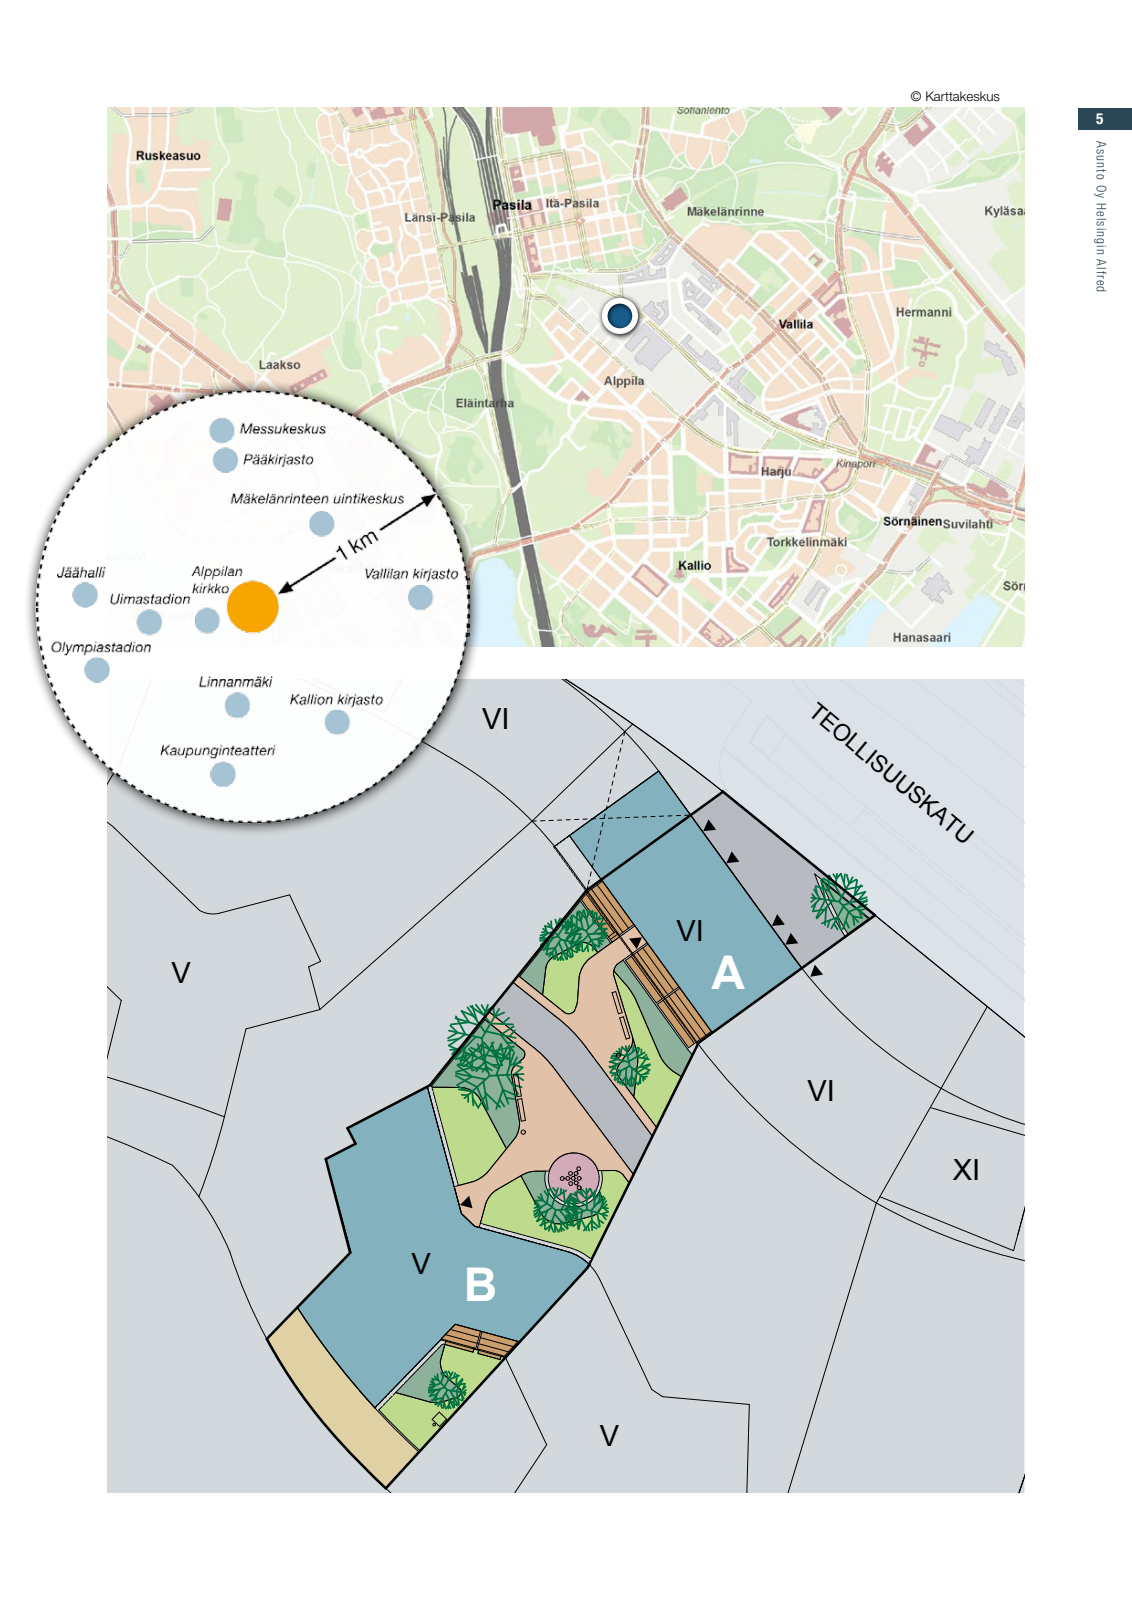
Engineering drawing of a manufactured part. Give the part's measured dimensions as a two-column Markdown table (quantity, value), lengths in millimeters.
| quantity | value |
| --- | --- |
| STEP written by | ACIS (automotive_design) |
| units | millimeters |
| bodies | 2 solids, 29 faces (9 planar, 12 cylindrical, 8 other) |
| overall size | 101 × 6 × 6 |
| volume | 2 664 mm³ |
| surface area | 1 927 mm² |
| round bosses / shafts (diameter × count) | 6 × 1, 5.7 × 1 |
| partial cylindrical surfaces (radius × count) | 0.48 × 1, 0.79 × 1, 1.09 × 1, 2.9 × 1 |
| main face-to-face distances | 55.4, 13.4, 42, 0.31, 19.19, 5.79, 36.21 |
